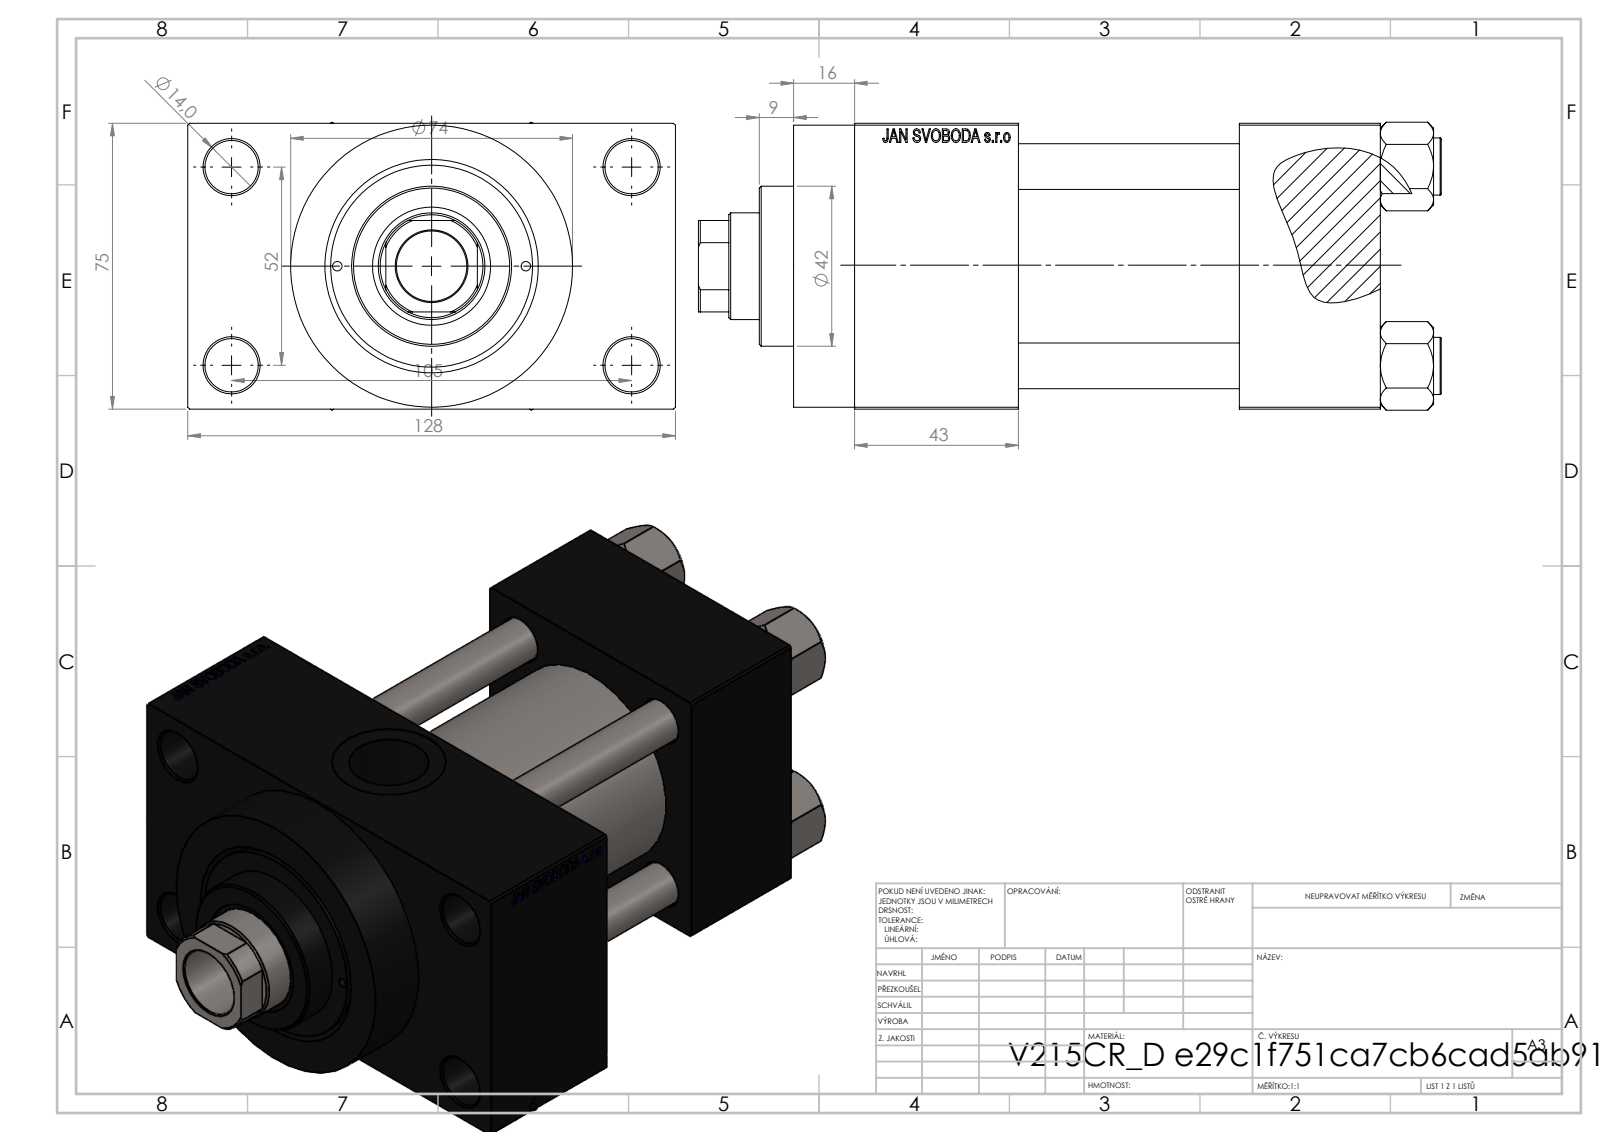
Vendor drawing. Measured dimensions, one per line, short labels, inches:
name: V215_VC_A; V215CR_D_TYCINKA; V215CR_D_Body; V215CR_VCP_D (+1 more)
written by: SolidWorks 2019 (CONFIG_CONTROL_DESIGN)
unit: in
bodies: 11 solids, 1112 faces (499 planar, 93 cylindrical, 520 other)
size: 7.677 × 5.039 × 2.974
volume: 49.74 in³; area: 261.6 in²
holes: 4× ⌀0.472, 4× ⌀0.551, 2× ⌀0.098, 2× ⌀0.276, 2× ⌀0.825, 2× ⌀1.181, 1× ⌀0.728, 1× ⌀1.102, 1× ⌀1.22, 1× ⌀1.614, 1× ⌀1.969, 1× ⌀2.087
bosses: 4× ⌀0.591, 1× ⌀2.913, 1× ⌀2.205, 1× ⌀1.654
rounds: 1× R0.531
face distances: 2.953, 2.283, 1.457, 3.74, 1.043, 3.996, 5.433, 3.976, 1.693, 0.63
hole spacings: 1.031, 1.037, 1.456, 1.497, 2.059, 2.253, 2.3, 2.307
